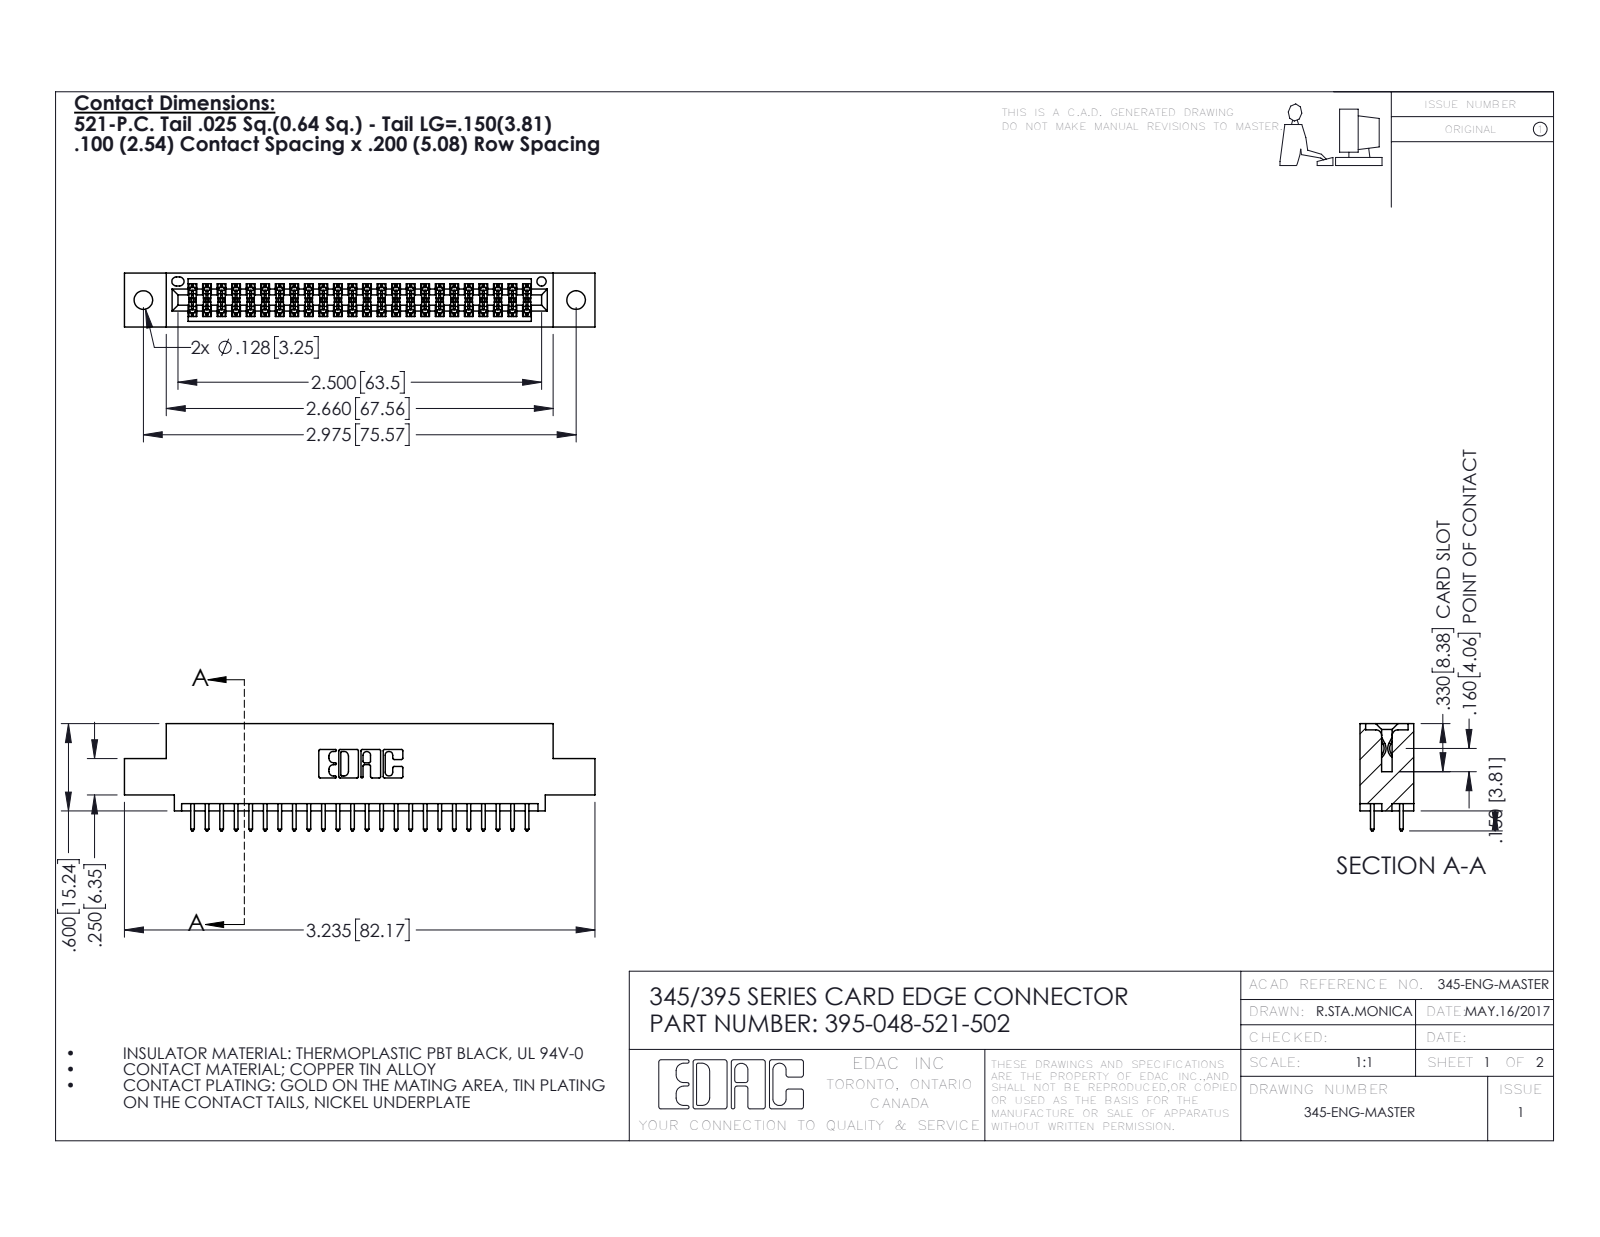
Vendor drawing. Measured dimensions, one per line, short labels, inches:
name: 345 Part_0.110 Offset - 0.128 Dia; 395-048-521-502; 345-292-001_345-293-121
written by: SolidWorks 2016 (CONFIG_CONTROL_DESIGN)
unit: in
bodies: 49 solids, 2530 faces (1668 planar, 862 cylindrical, 0 other)
size: 3.235 × 0.737 × 0.37
volume: 0.469 in³; area: 16.59 in²
holes: 2× ⌀0.128, 1× ⌀0.064
rounds: 72× R0.006, 48× R0.01, 22× R0.01, 6× R0.007, 6× R0.031, 3× R0.026, 2× R0.014, 2× R0.019
face distances: 0.298, 0.072, 0.2, 0.37, 0.098, 0.272, 0.025, 0.225, 0.175, 0.149
hole spacings: 0.27, 2.741, 2.975
